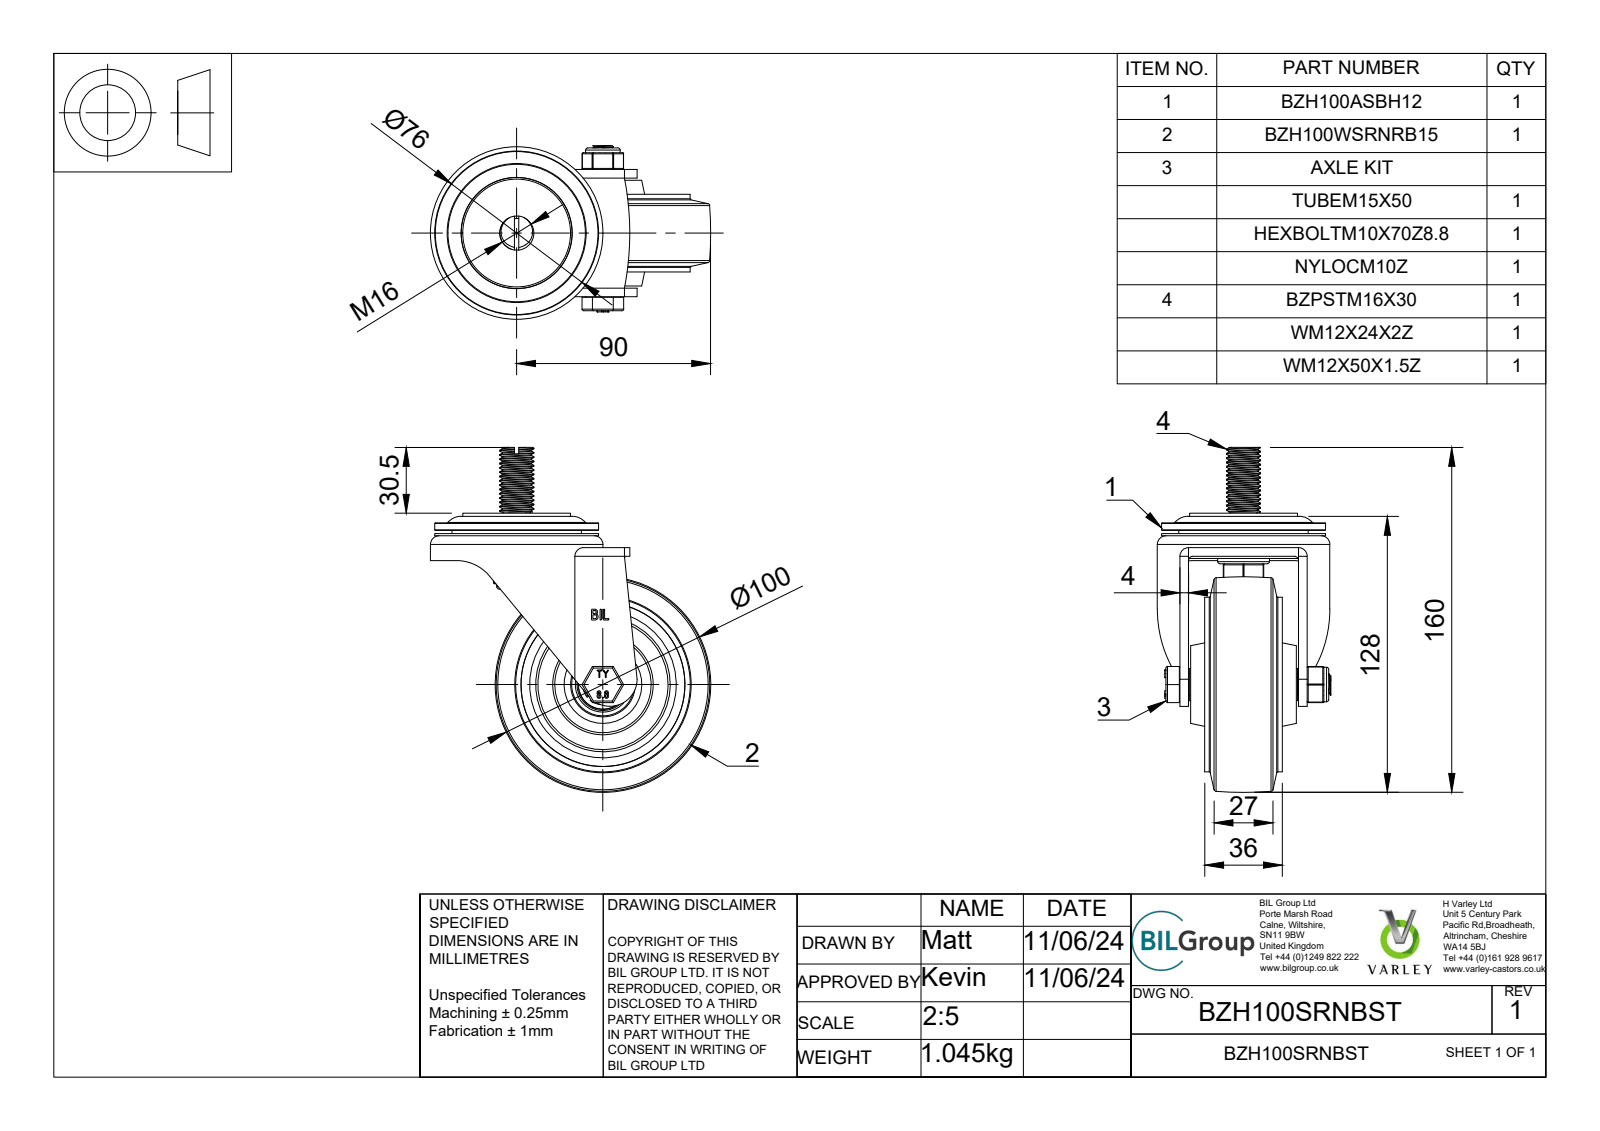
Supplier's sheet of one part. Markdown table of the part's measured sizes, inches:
| quantity | value |
| --- | --- |
| part name | BZH100SRNBST v3; BZH100ASBH12 v1; ZINC PLATED, PRESSED STEEL TOP PLATE; BEARING SEAL (+7 more) |
| STEP written by | Autodesk Translation Framework v13.14.0.145 (AUTOMOTIVE_DESIGN) |
| units | inches |
| bodies | 23 solids, 571 faces (219 planar, 227 cylindrical, 125 other) |
| overall size | 6.299 × 5.118 × 3.169 |
| volume | 19.38 in³ |
| surface area | 206.5 in² |
| round holes (diameter × count) | 0.472 × 2, 0.394 × 1, 0.404 × 1, 0.413 × 1, 0.476 × 1, 0.512 × 1, 0.531 × 1, 0.551 × 1, 0.591 × 1, 0.906 × 1, 1.181 × 1, 1.26 × 1 |
| round bosses / shafts (diameter × count) | 0.157 × 8, 3.189 × 1, 3.15 × 1, 2.992 × 1, 2.362 × 1, 1.988 × 1, 1.969 × 1, 1.535 × 1 |
| partial cylindrical surfaces (radius × count) | 0.02 × 36, 0.03 × 6, 0.079 × 4, 0.157 × 2, 0.369 × 1, 0.497 × 1, 0.787 × 1, 5.169 × 1 |
| main face-to-face distances | 0.256, 0.157, 0.453, 0.059, 0.295, 0.197, 0.315, 0.413, 0.098, 0.827 |
